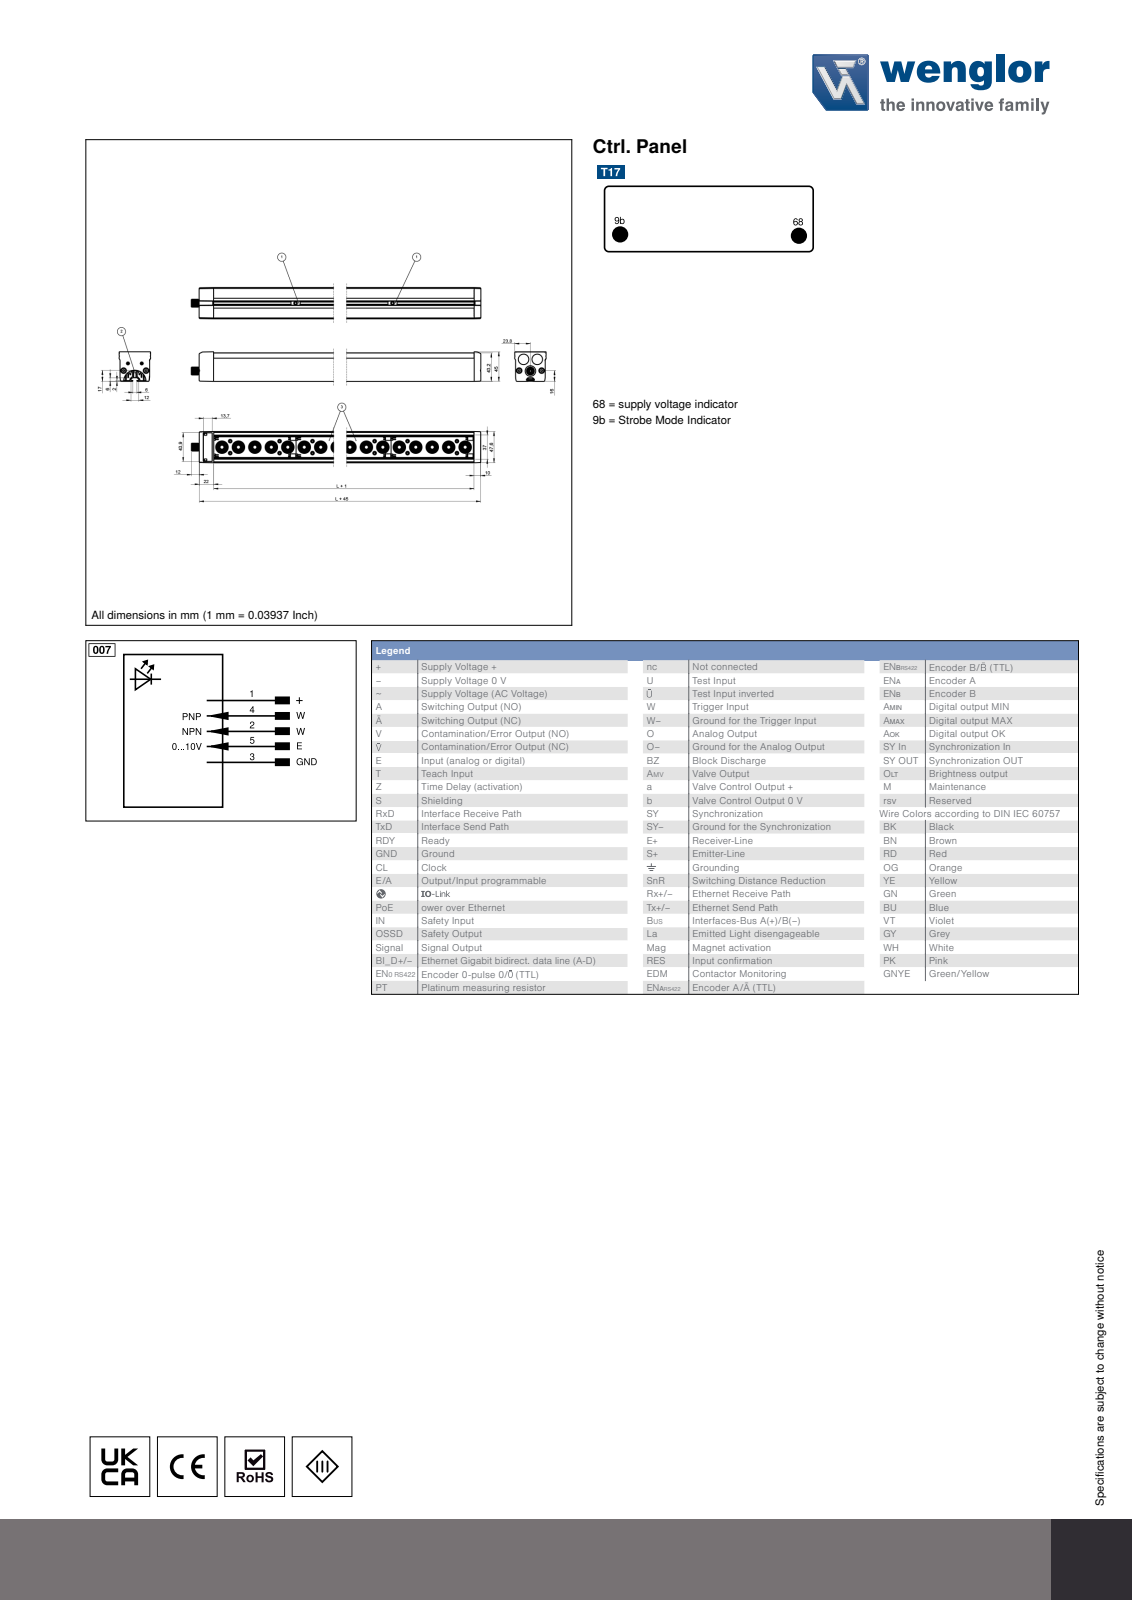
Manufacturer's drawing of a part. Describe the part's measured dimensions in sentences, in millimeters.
The part is named "OPT2402 and OPT2406". Its 3-D file was written by "SolidWorks 2021 (AUTOMOTIVE_DESIGN)". It is 3 solids with 491 faces: 230 planar, 152 cylindrical and 109 other. Overall it measures 420.1 by 47.6 by 45 millimeters. Its volume is 721 500 cubic millimeters and its surface area 92 450 square millimeters. Round holes: 2 of diameter 3.3, 2 of diameter 8.5, 1 of diameter 8.3. Round bosses or shafts: 5 of diameter 1, 4 of diameter 7, 2 of diameter 5.4, 1 of diameter 12, 1 of diameter 10.7. Partial cylindrical surfaces (rounded edges, fillets, slot ends): 32 of radius 0.5, 26 of radius 0.2, 20 of radius 1, 4 of radius 0.4, 4 of radius 1.2, 4 of radius 1.5, 3 of radius 0.6, 2 of radius 0.3. The main face-to-face distances are 39.8, 45, 1.5, 44.9, 38.3, 407.2, 40.8, 37.6, 5.5, 44.7. The hole center spacings are 17.1, 34.1, 175.4.
